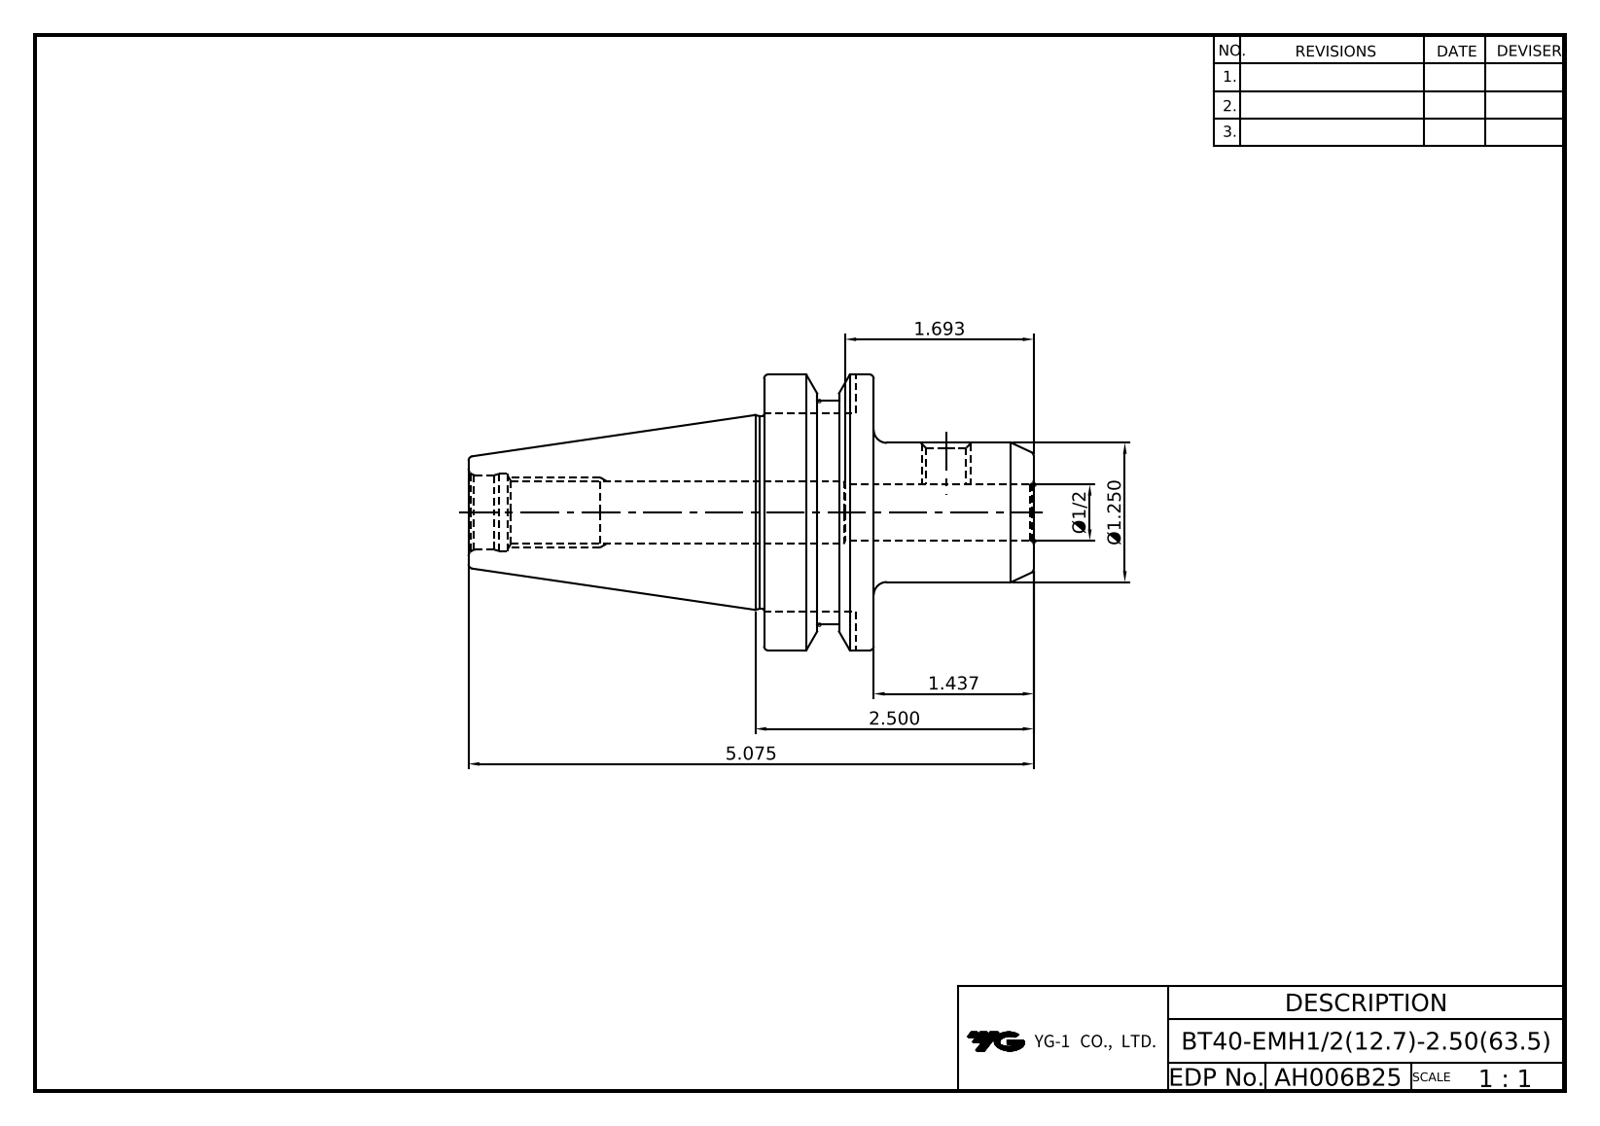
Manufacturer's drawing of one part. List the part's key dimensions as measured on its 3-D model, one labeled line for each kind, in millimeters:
Part name (STEP PRODUCT): LO-BT40-EMH12.7-63.5
STEP written by: Autodesk Inventor 2022 (AUTOMOTIVE_DESIGN)
Units: millimetres
Bodies: 1 solid, 49 faces (15 planar, 15 cylindrical, 19 other)
Overall size (bounding box): 128.9 × 63 × 63
Volume: 143 037 mm³ · Surface area: 27 317 mm²
Round holes (diameter × count): ⌀9.73 ×1, ⌀12.7 ×1, ⌀13.5 ×1, ⌀13.84 ×1, ⌀17 ×1, ⌀17.6 ×1
Round bosses / shafts (diameter × count): ⌀63 ×1, ⌀52.6 ×1, ⌀44 ×1, ⌀31.75 ×1
Partial cylindrical surfaces — rounded edges, fillets, slot ends (radius × count): R8.05 ×1
Main face-to-face distances: 25, 61.5, 36.5, 45.2, 16.1, 67.4, 92.4, 128.9, 84.5, 17.1
